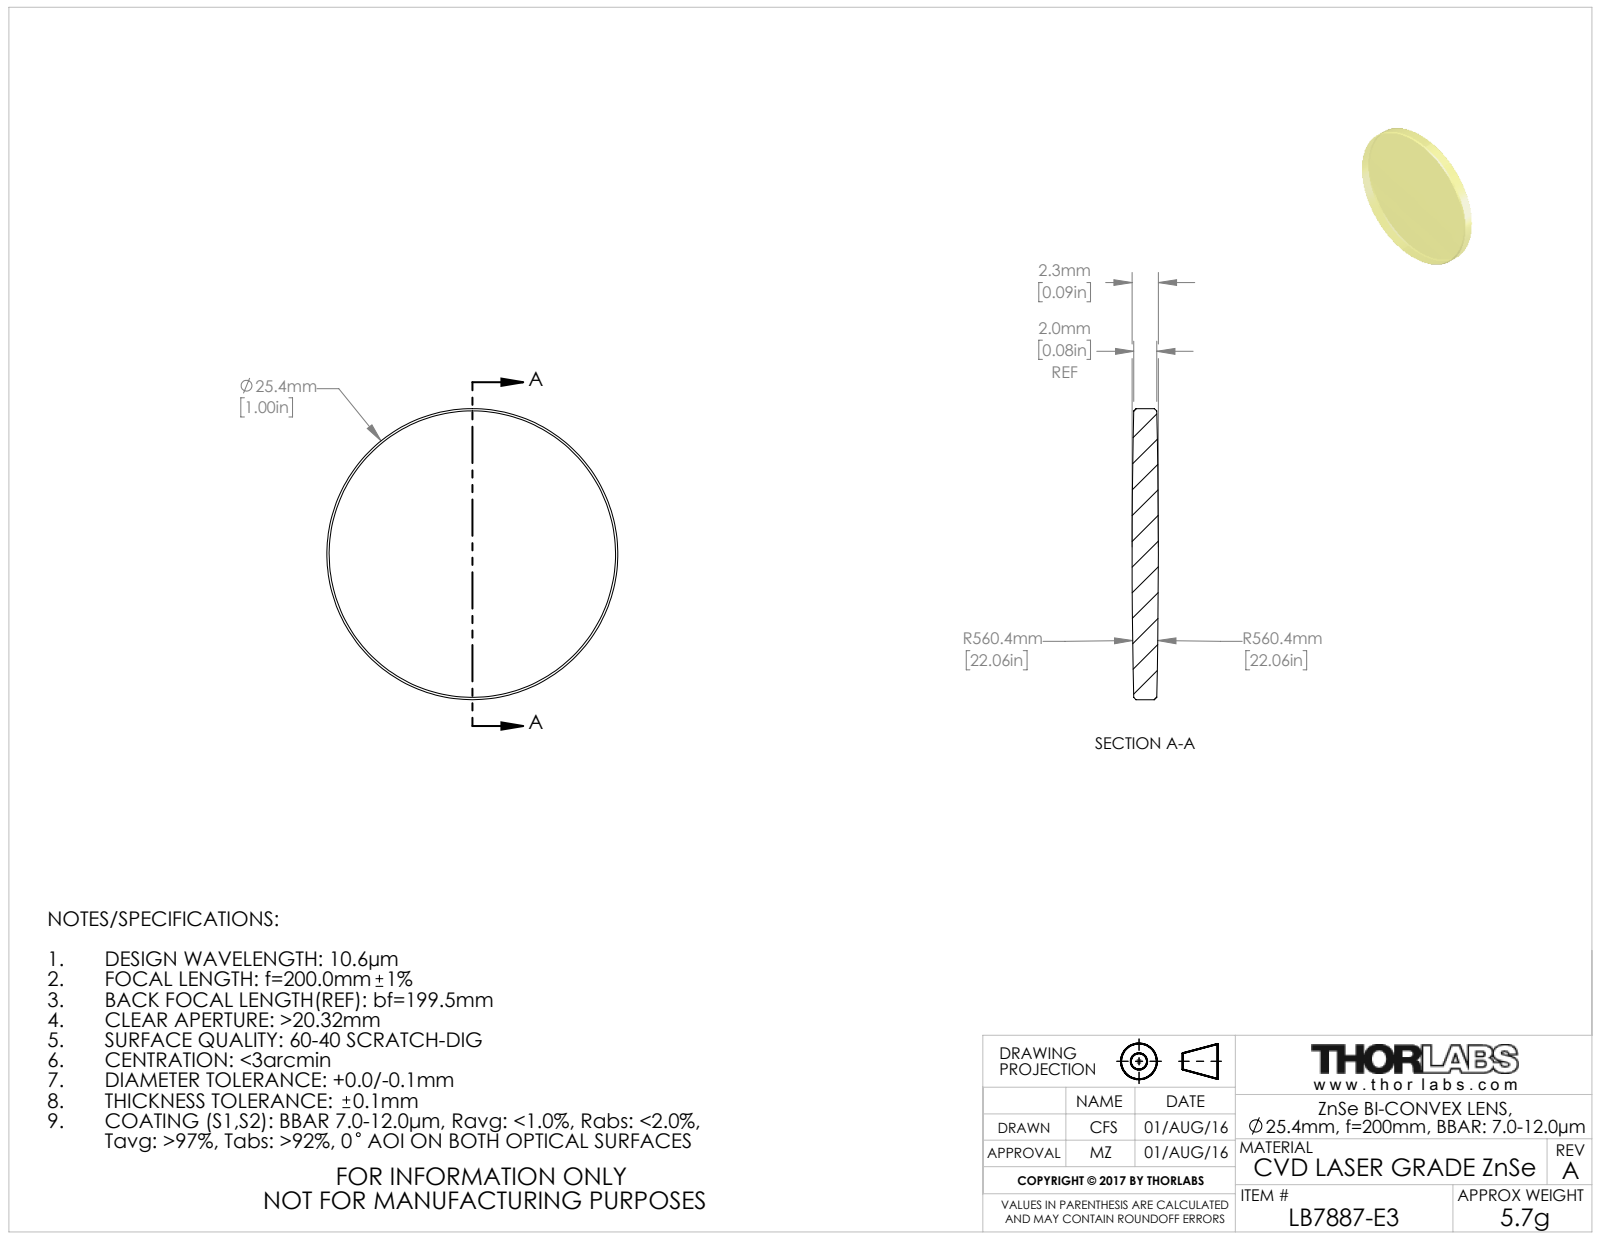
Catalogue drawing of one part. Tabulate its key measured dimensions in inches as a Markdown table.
| quantity | value |
| --- | --- |
| part name | TTN051896-E0W |
| STEP written by | SolidWorks 2016 (CONFIG_CONTROL_DESIGN) |
| units | inches |
| bodies | 1 solid, 10 faces (0 planar, 2 cylindrical, 8 other) |
| overall size | 1 × 1 × 0.09 |
| volume | 0.066 in³ |
| surface area | 1.79 in² |
| round bosses / shafts (diameter × count) | 1 × 1 |
